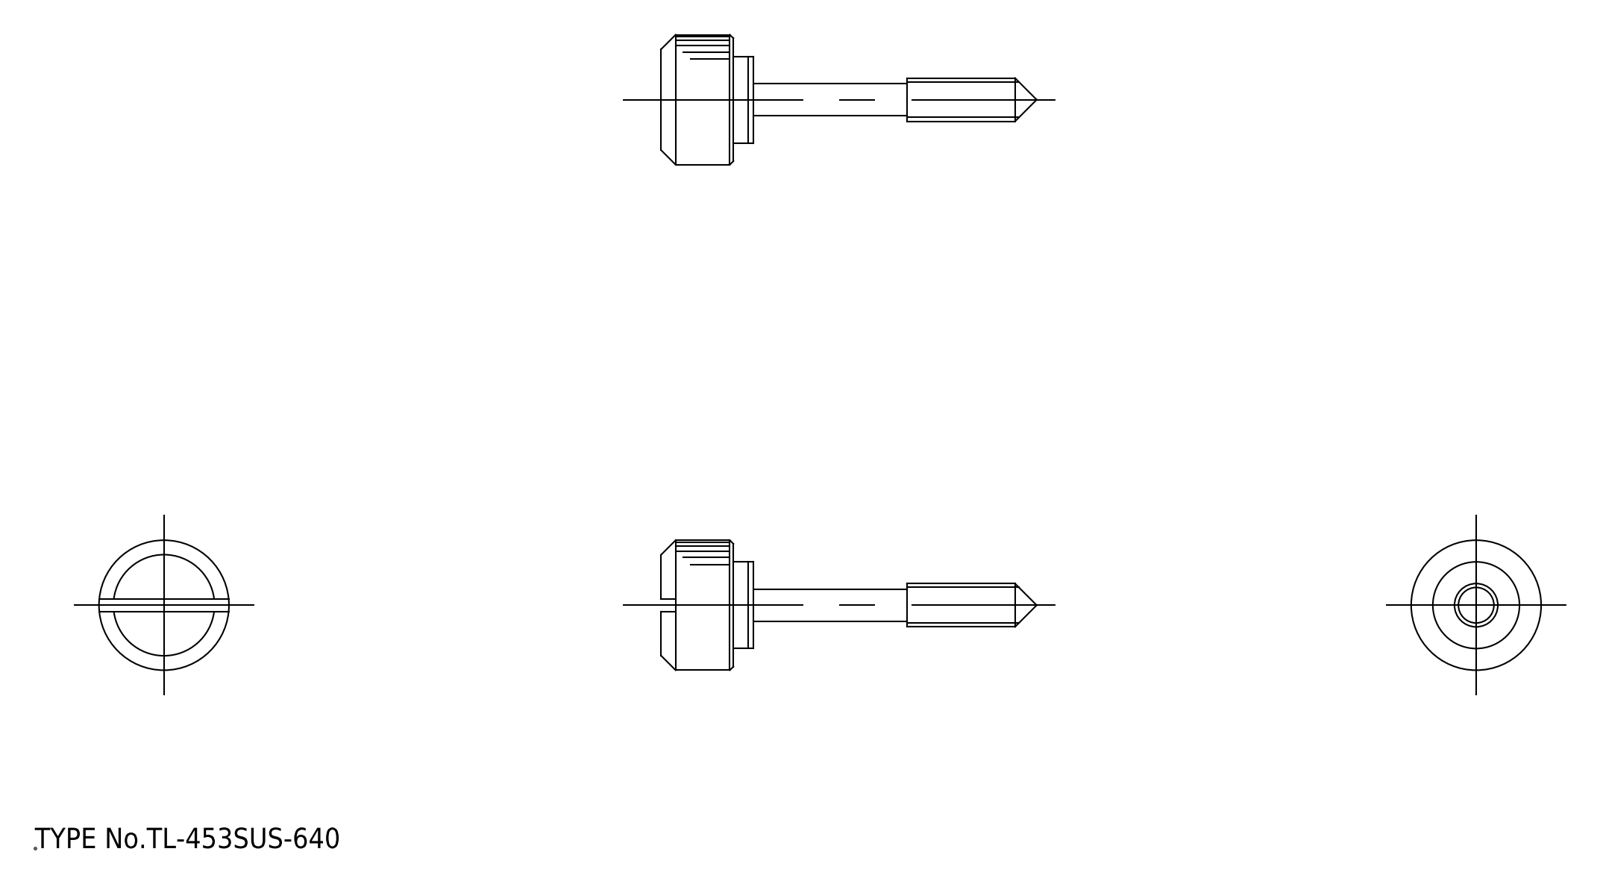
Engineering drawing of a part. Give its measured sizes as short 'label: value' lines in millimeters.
name: washer; knob
written by: spGate 19.8.4 (****-****-****-****) (AUTOMOTIVE_DESIGN)
unit: mm
bodies: 2 solids, 42 faces (18 planar, 18 cylindrical, 6 other)
size: 52 × 18 × 18
volume: 3 474 mm³; area: 1 972 mm²
bosses: 1× ⌀18, 1× ⌀12, 1× ⌀6, 1× ⌀4.5
rounds: 4× R1, 1× R2.3
face distances: 2, 10, 12, 12.8, 2.8, 0.8, 8, 10.8, 1.8, 34
